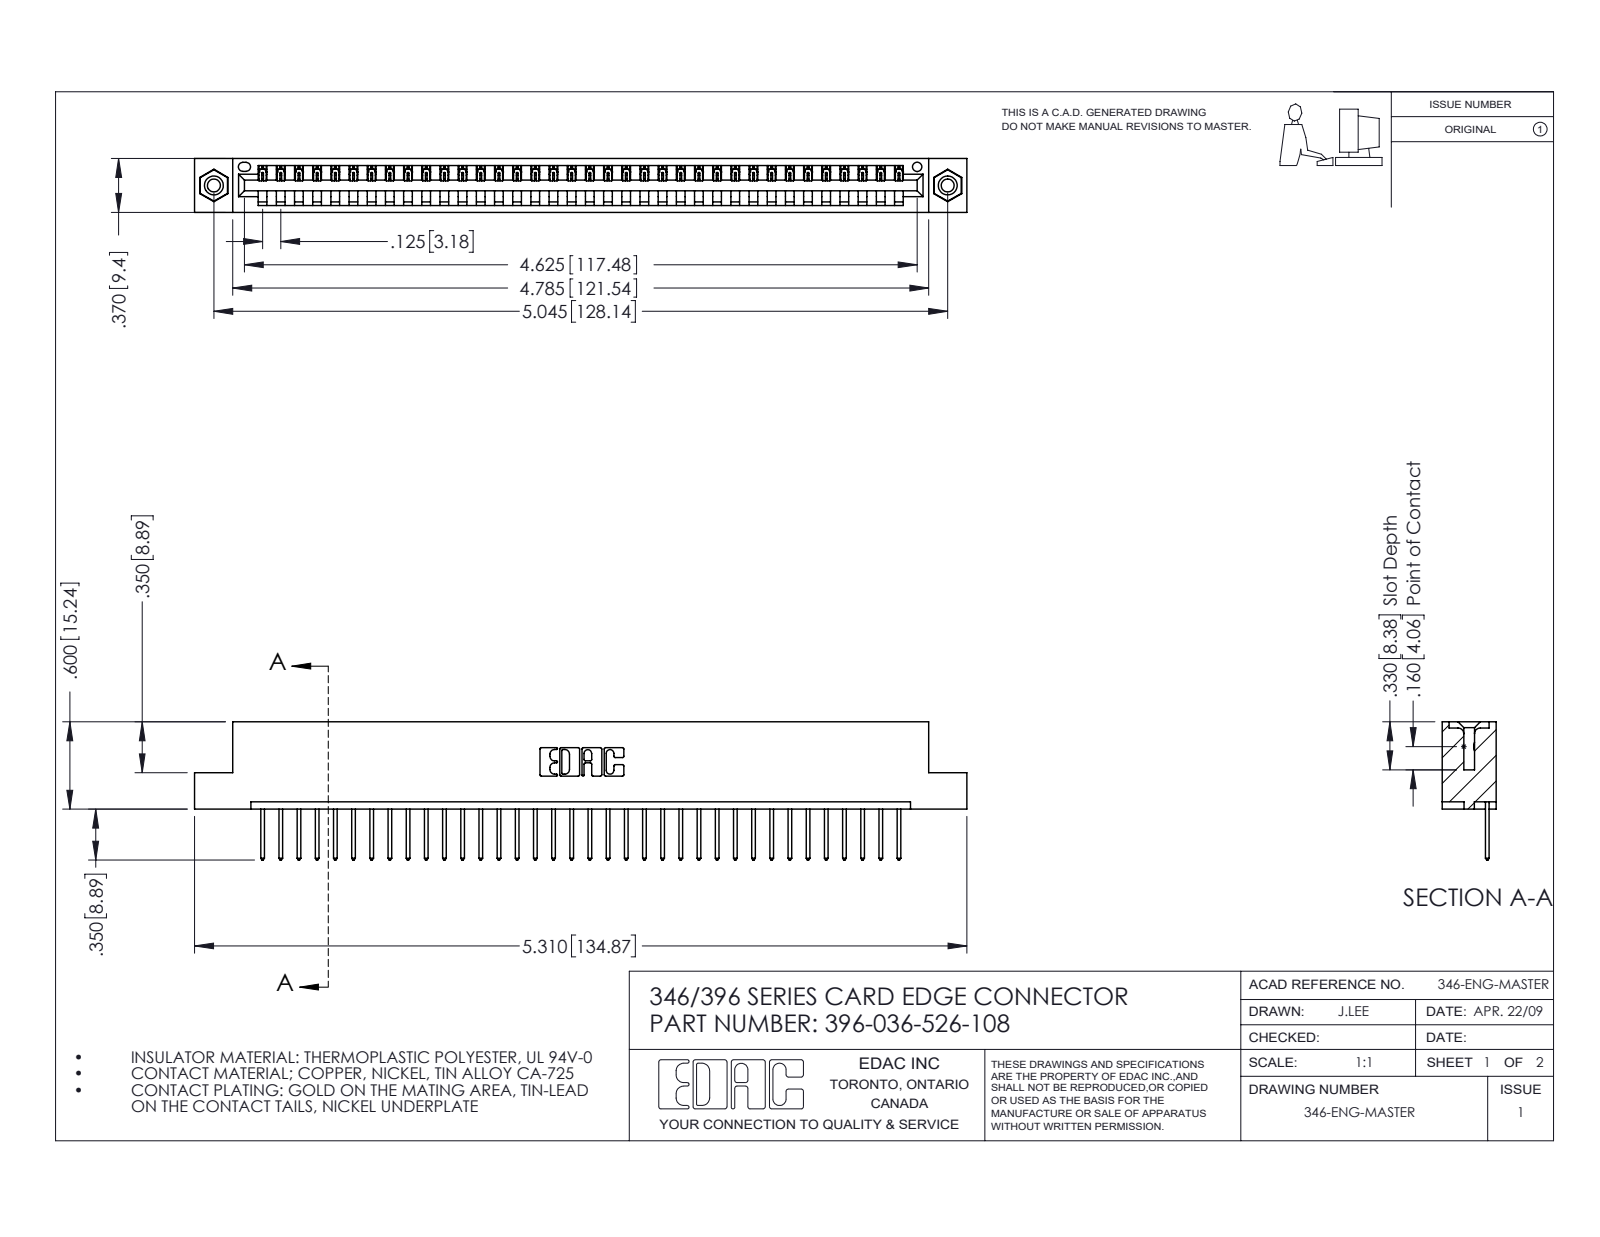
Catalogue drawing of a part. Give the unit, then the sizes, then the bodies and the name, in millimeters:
Units: millimetres
Overall size (bounding box): 134.9 × 24.1 × 9.4
Round holes (diameter × count): ⌀2.3 ×2, ⌀3.2 ×2, ⌀4 ×2, ⌀1.6 ×1
Round bosses / shafts (diameter × count): ⌀3.9 ×2
Partial cylindrical surfaces — rounded edges, fillets, slot ends (radius × count): R0.2 ×72, R0.3 ×72, R0.3 ×22, R0.2 ×6, R0.8 ×6, R0.7 ×3, R0.8 ×2, R1 ×2
Main face-to-face distances: 1.2, 8.2, 9.4, 6.4, 1.8, 7.6, 0.6, 3.8, 5.6, 2.5
Hole centre spacings: 6.2, 122.8, 128.1
Volume: 12 800 mm³ · Surface area: 15 960 mm²
Bodies: 39 solids, 2270 faces (1548 planar, 706 cylindrical, 16 other)
Part name (STEP PRODUCT): 345-292-001_345-293-126; 346 Part_Flush Mounting Lugs - 0.156 Dia-TI; 345-250-001_345-250-003-102; 396-036-526-108
STEP written by: SolidWorks 2016 (CONFIG_CONTROL_DESIGN)
